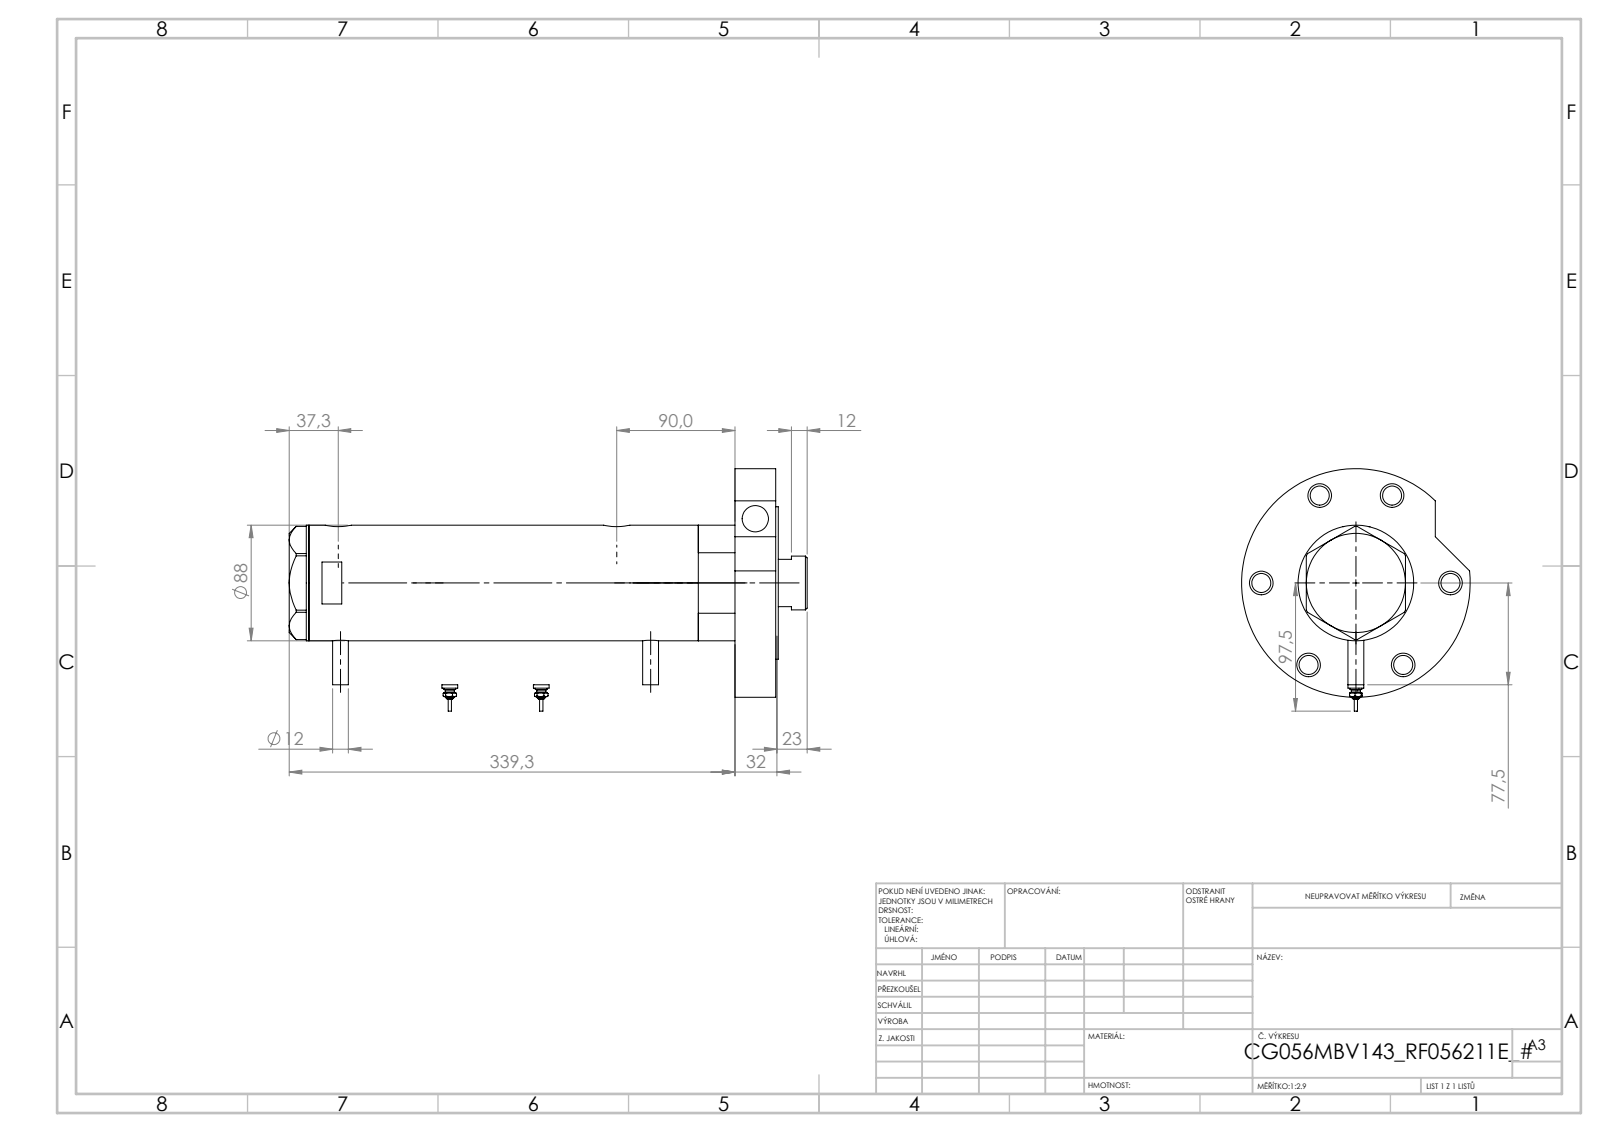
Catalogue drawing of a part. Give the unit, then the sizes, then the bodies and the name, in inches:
Units: inches
Overall size (bounding box): 15.524 × 7.264 × 6.85
Round holes (diameter × count): ⌀0.571 ×7, ⌀0.709 ×6, ⌀0.787 ×3, ⌀0.492 ×2, ⌀0.518 ×2, ⌀1.654 ×1, ⌀1.713 ×1, ⌀2.205 ×1, ⌀2.362 ×1, ⌀2.953 ×1, ⌀3.15 ×1
Round bosses / shafts (diameter × count): ⌀0.472 ×4, ⌀0.354 ×2, ⌀0.276 ×2, ⌀0.177 ×2, ⌀0.098 ×2, ⌀6.85 ×1, ⌀4.567 ×1, ⌀3.465 ×1
Main face-to-face distances: 1.22, 0.079, 14.067, 12.768, 13.988, 1.299, 9.228, 3.539, 4.76, 4.839
Hole centre spacings: 2.835, 3.15, 4.714, 4.91, 5.085, 5.657, 0.067, 1.016
Volume: 156.7 in³ · Surface area: 559.5 in²
Bodies: 7 solids, 257 faces (91 planar, 102 cylindrical, 64 other)
Part name (STEP PRODUCT): V270CG_VC; V270CG_RF211E; V270CG_MIDDLE; V270CG_BACK (+2 more)
STEP written by: SolidWorks 2019 (CONFIG_CONTROL_DESIGN)
